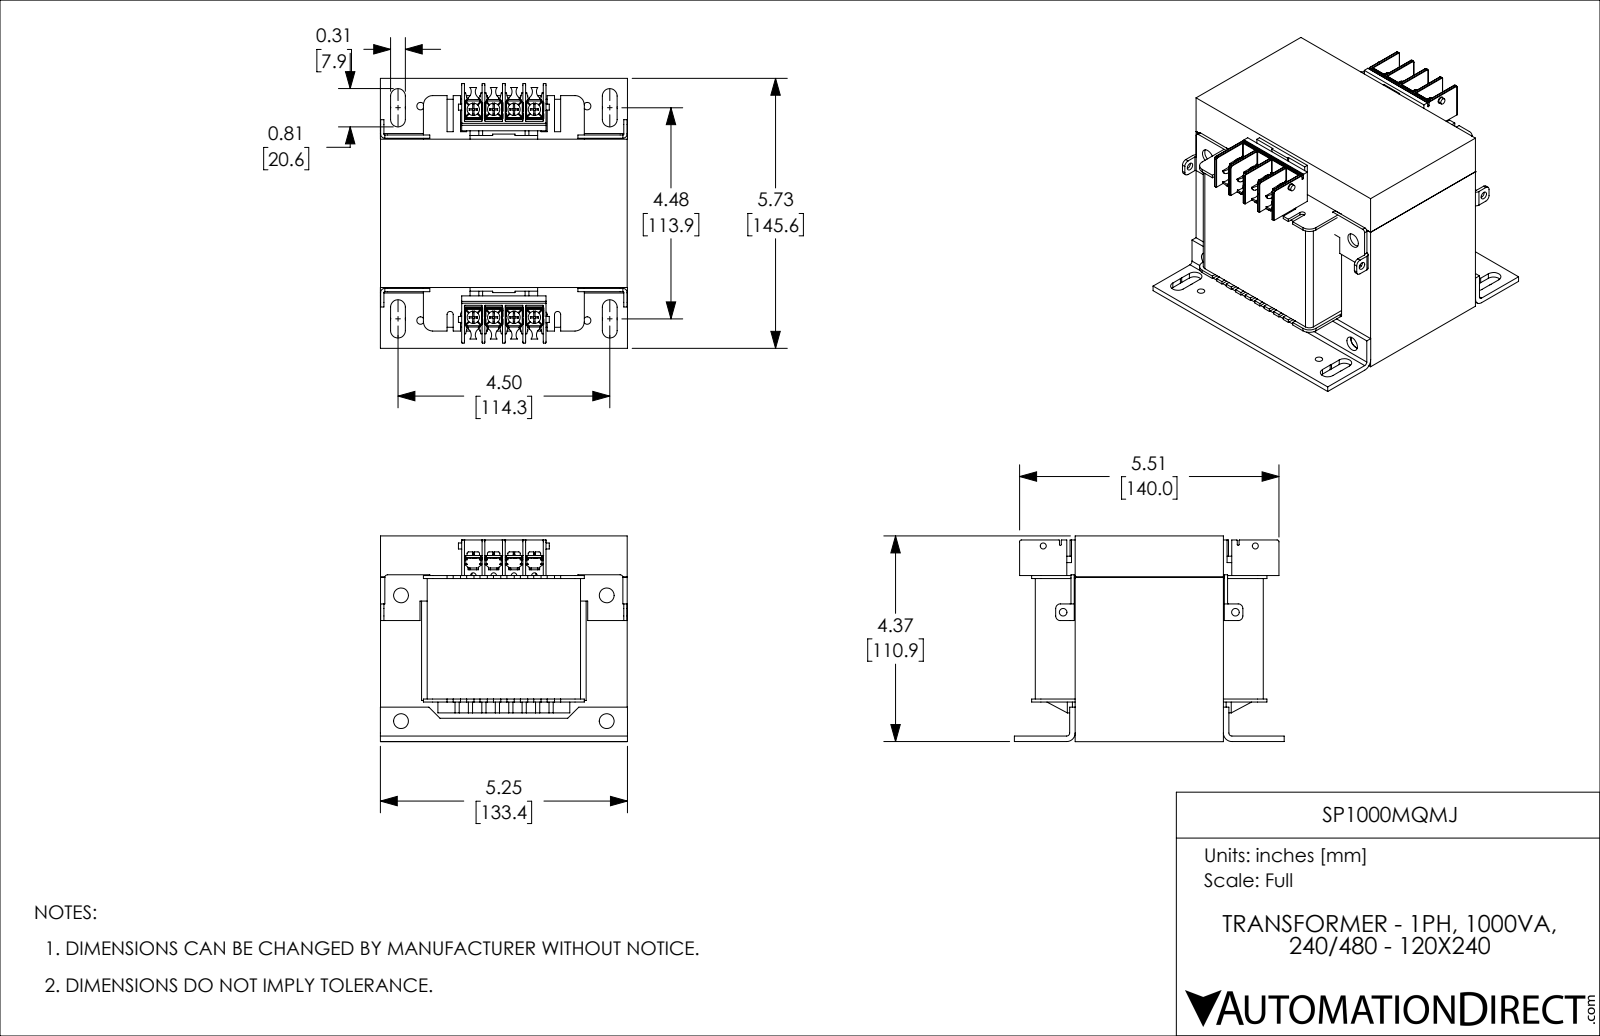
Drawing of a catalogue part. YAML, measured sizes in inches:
part_name: "SP1000MQMJ"
step_written_by: "SolidWorks 2018 (AUTOMOTIVE_DESIGN)"
units: inches
bodies: {solids: 42, faces: 3344, planar: 2113, cylindrical: 937, other: 294}
overall_size: [5.734, 5.25, 4.37]
volume: 88.01
surface_area: 372.7
round_holes:
  - {diameter: 0.157, count: 12}
  - {diameter: 0.105, count: 8}
  - {diameter: 0.138, count: 8}
  - {diameter: 0.315, count: 4}
  - {diameter: 0.1, count: 2}
  - {diameter: 0.161, count: 2}
  - {diameter: 0.177, count: 2}
round_bosses_or_shafts:
  - {diameter: 0.262, count: 8}
  - {diameter: 0.24, count: 8}
  - {diameter: 0.168, count: 8}
  - {diameter: 0.11, count: 8}
  - {diameter: 0.128, count: 2}
partial_cylinders:
  - {radius: 0.005, count: 52}
  - {radius: 0.01, count: 52}
  - {radius: 0.012, count: 38}
  - {radius: 0.029, count: 32}
  - {radius: 0.157, count: 20}
  - {radius: 0.035, count: 12}
  - {radius: 0.079, count: 10}
  - {radius: 0.065, count: 9}
face_to_face_distances: [0.874, 3.496, 4.37, 0.118, 3.15, 1.748, 0.992, 4.252, 2.622, 3.378]
hole_center_spacings: [0.433, 0.866, 4.429, 1.299, 4.407, 4.492, 4.419, 4.439]
